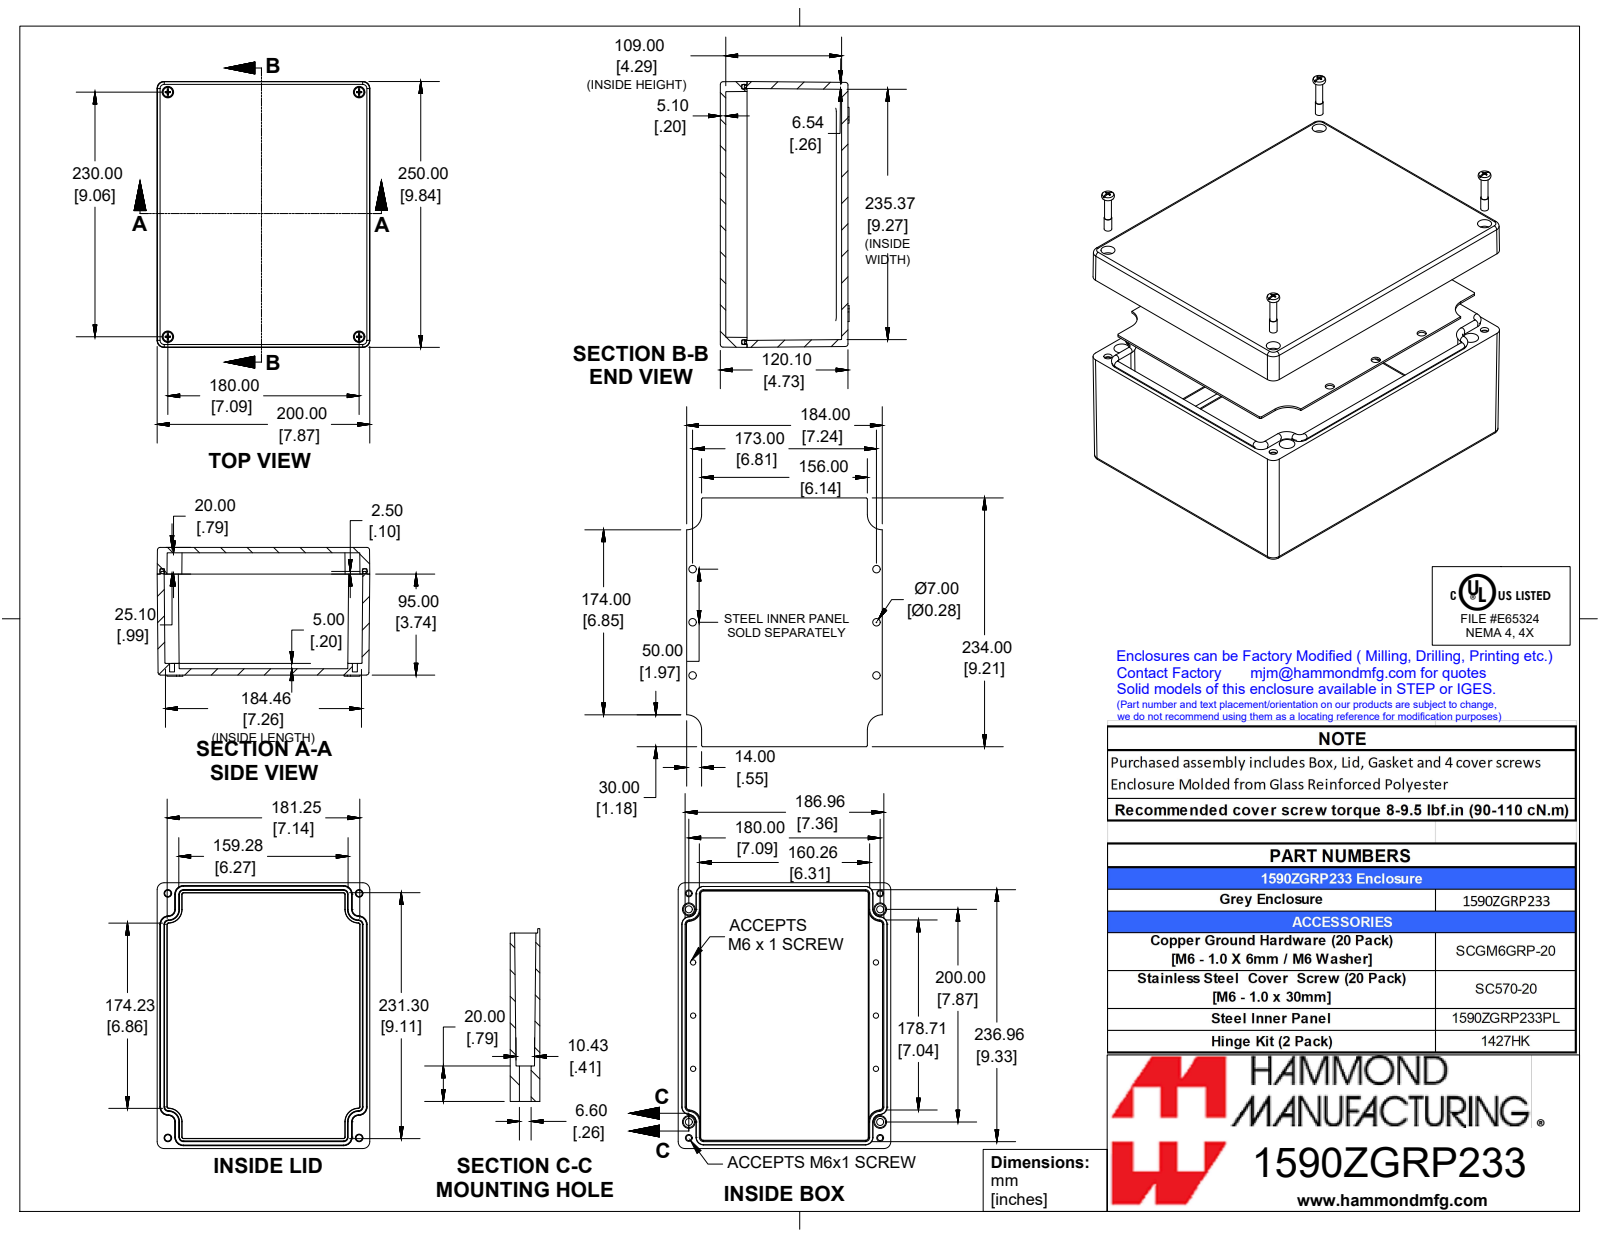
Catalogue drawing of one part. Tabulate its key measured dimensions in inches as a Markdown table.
| quantity | value |
| --- | --- |
| part name | 1590ZGRP233 |
| STEP written by | SolidWorks 2019 (CONFIG_CONTROL_DESIGN) |
| units | inches |
| bodies | 8 solids, 495 faces (253 planar, 90 cylindrical, 152 other) |
| overall size | 9.843 × 7.874 × 4.768 |
| volume | 86.81 in³ |
| surface area | 802.7 in² |
| round holes (diameter × count) | 0.194 × 10, 0.276 × 6, 0.236 × 4, 0.252 × 4, 0.26 × 4, 0.425 × 4 |
| round bosses / shafts (diameter × count) | 0.181 × 6, 0.231 × 4, 0.208 × 4 |
| partial cylindrical surfaces (radius × count) | 0.02 × 18, 0.098 × 8, 0.253 × 8, 0.551 × 4 |
| main face-to-face distances | 0.257, 4.728, 0.433, 4.295, 0.493, 0.06, 4.235, 4.528, 4.094, 4.035 |
| hole center spacings | 1.969, 3.937, 7.071, 0.02, 6.791, 0.591, 1.973, 1.975 |
